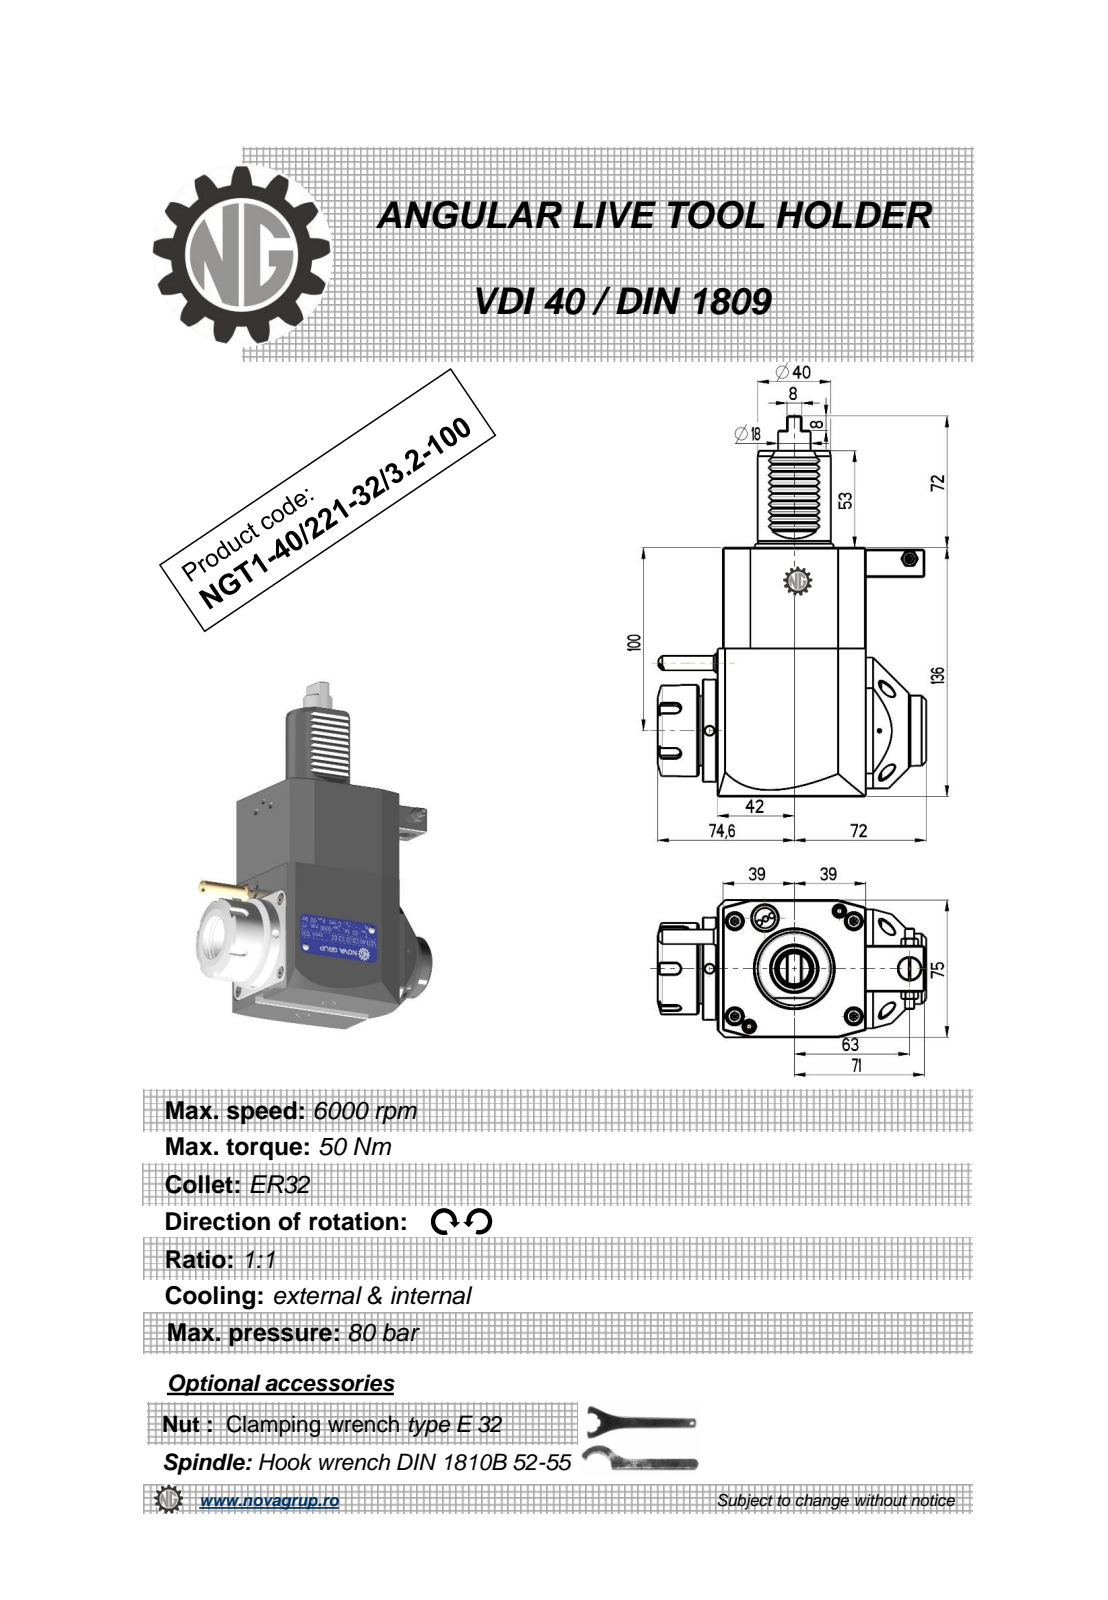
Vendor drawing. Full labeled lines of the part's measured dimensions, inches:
Part name (STEP PRODUCT): NGT1_40_221_32_3_2_100
STEP written by: PRO/ENGINEER BY PARAMETRIC TECHNOLOGY CORPORATION, 2010280 (CONFIG_CONTROL_DESIGN)
Units: inches
Bodies: 1 solid, 418 faces (190 planar, 91 cylindrical, 137 other)
Overall size (bounding box): 8.189 × 5.772 × 2.953
Volume: 62.12 in³ · Surface area: 121.5 in²
Round holes (diameter × count): ⌀0.197 ×3, ⌀0.118 ×1, ⌀0.165 ×1, ⌀0.177 ×1, ⌀0.374 ×1, ⌀0.472 ×1, ⌀1.063 ×1
Round bosses / shafts (diameter × count): ⌀2.205 ×1, ⌀1.969 ×1, ⌀1.693 ×1, ⌀1.575 ×1, ⌀1.516 ×1, ⌀0.701 ×1, ⌀0.441 ×1, ⌀0.353 ×1
Partial cylindrical surfaces — rounded edges, fillets, slot ends (radius × count): R0.01 ×12, R0.012 ×10, R0.009 ×6, R0.118 ×5, R0.031 ×2, R0.02 ×1, R1.575 ×1
Main face-to-face distances: 2.953, 5.354, 3.071, 3.189, 0.118, 3.342, 0.11, 3.181, 0.295, 0.02
Hole centre spacings: 1.611, 2.291, 3.642, 4.301, 5.674
